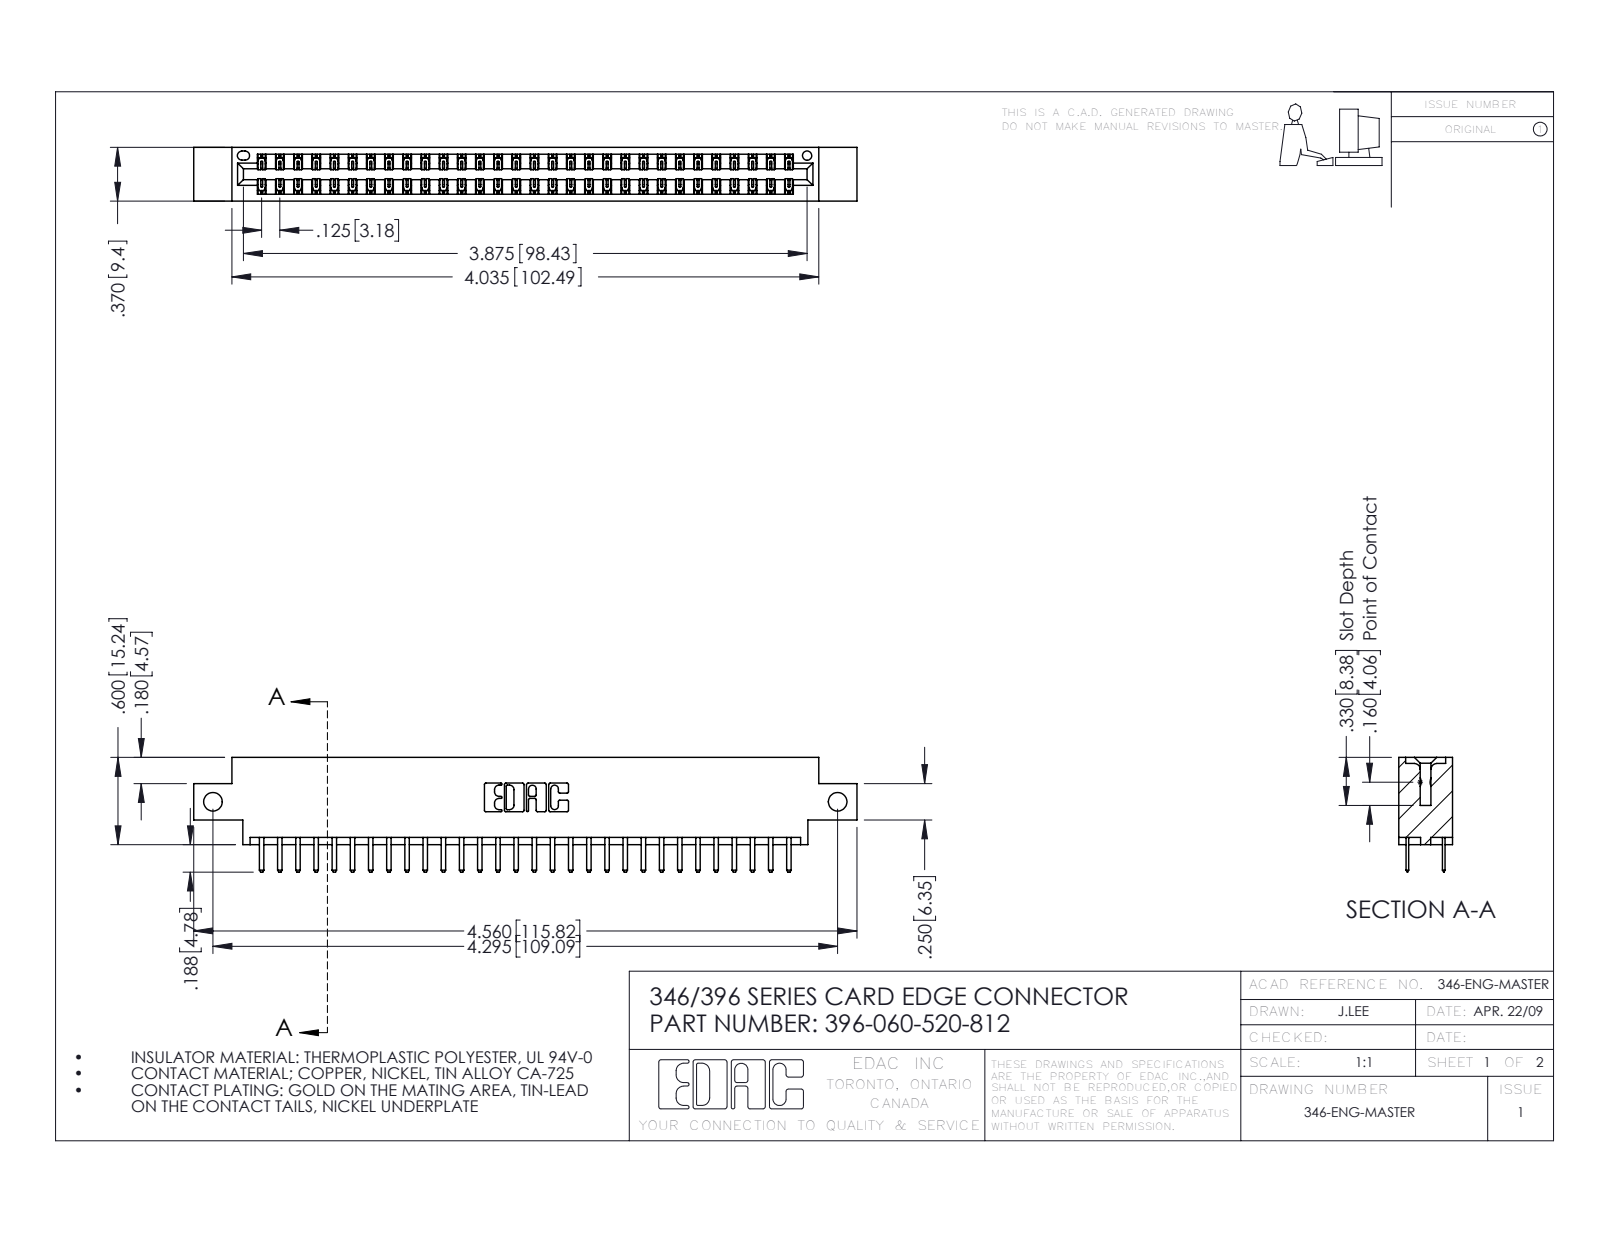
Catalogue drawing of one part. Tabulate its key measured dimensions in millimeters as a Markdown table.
| quantity | value |
| --- | --- |
| part name | 345-292-001_345-293-120; 346 Part_0.170 Offset - Side Mount; 396-060-520-812 |
| STEP written by | SolidWorks 2016 (CONFIG_CONTROL_DESIGN) |
| units | millimeters |
| bodies | 61 solids, 3486 faces (2300 planar, 1186 cylindrical, 0 other) |
| overall size | 115.8 × 20 × 9.4 |
| volume | 10 900 mm³ |
| surface area | 14 820 mm² |
| round holes (diameter × count) | 3.3 × 2, 1.6 × 1 |
| partial cylindrical surfaces (radius × count) | 0.2 × 90, 0.3 × 64, 0.3 × 22, 0.2 × 6, 0.8 × 6, 0.7 × 3, 0.4 × 2, 0.6 × 2 |
| main face-to-face distances | 1.2, 8.2, 6.4, 9.4, 7, 1.8, 7.6, 0.6, 3.8, 5.6 |
| hole center spacings | 109.1 |
